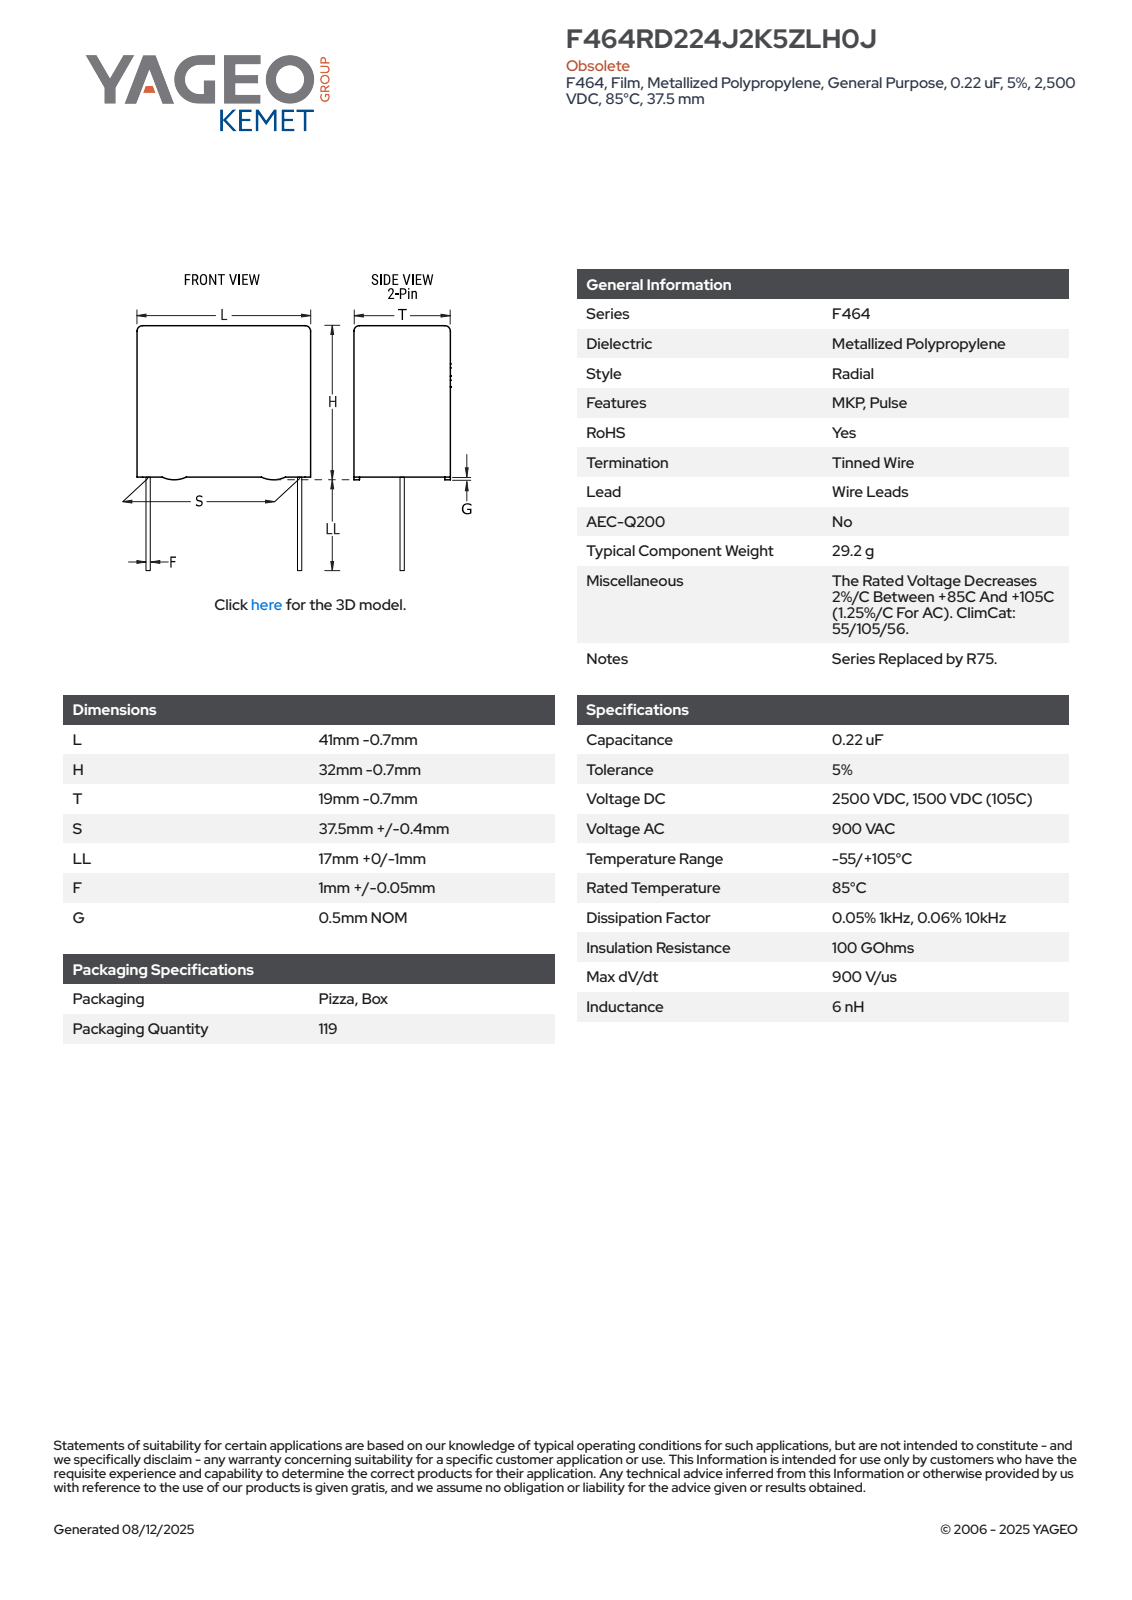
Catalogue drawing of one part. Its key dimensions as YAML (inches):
part_name: "CFR_RBG_41X32X19_L40.3H31.3T18.3S37.5LL17F1.05G0.5"
step_written_by: "SolidWorks 2014 (AUTOMOTIVE_DESIGN)"
units: inches
bodies: {solids: 4, faces: 89, planar: 81, cylindrical: 8, other: 0}
overall_size: [1.902, 1.587, 0.72]
volume: 1.388
surface_area: 8.336
round_bosses_or_shafts:
  - {diameter: 0.041, count: 2}
partial_cylinders:
  - {radius: 0.02, count: 4}
face_to_face_distances: [0.72, 1.213, 1.587, 0.721, 0.02, 1.232, 0.041, 0.68, 0.041, 0.639]
